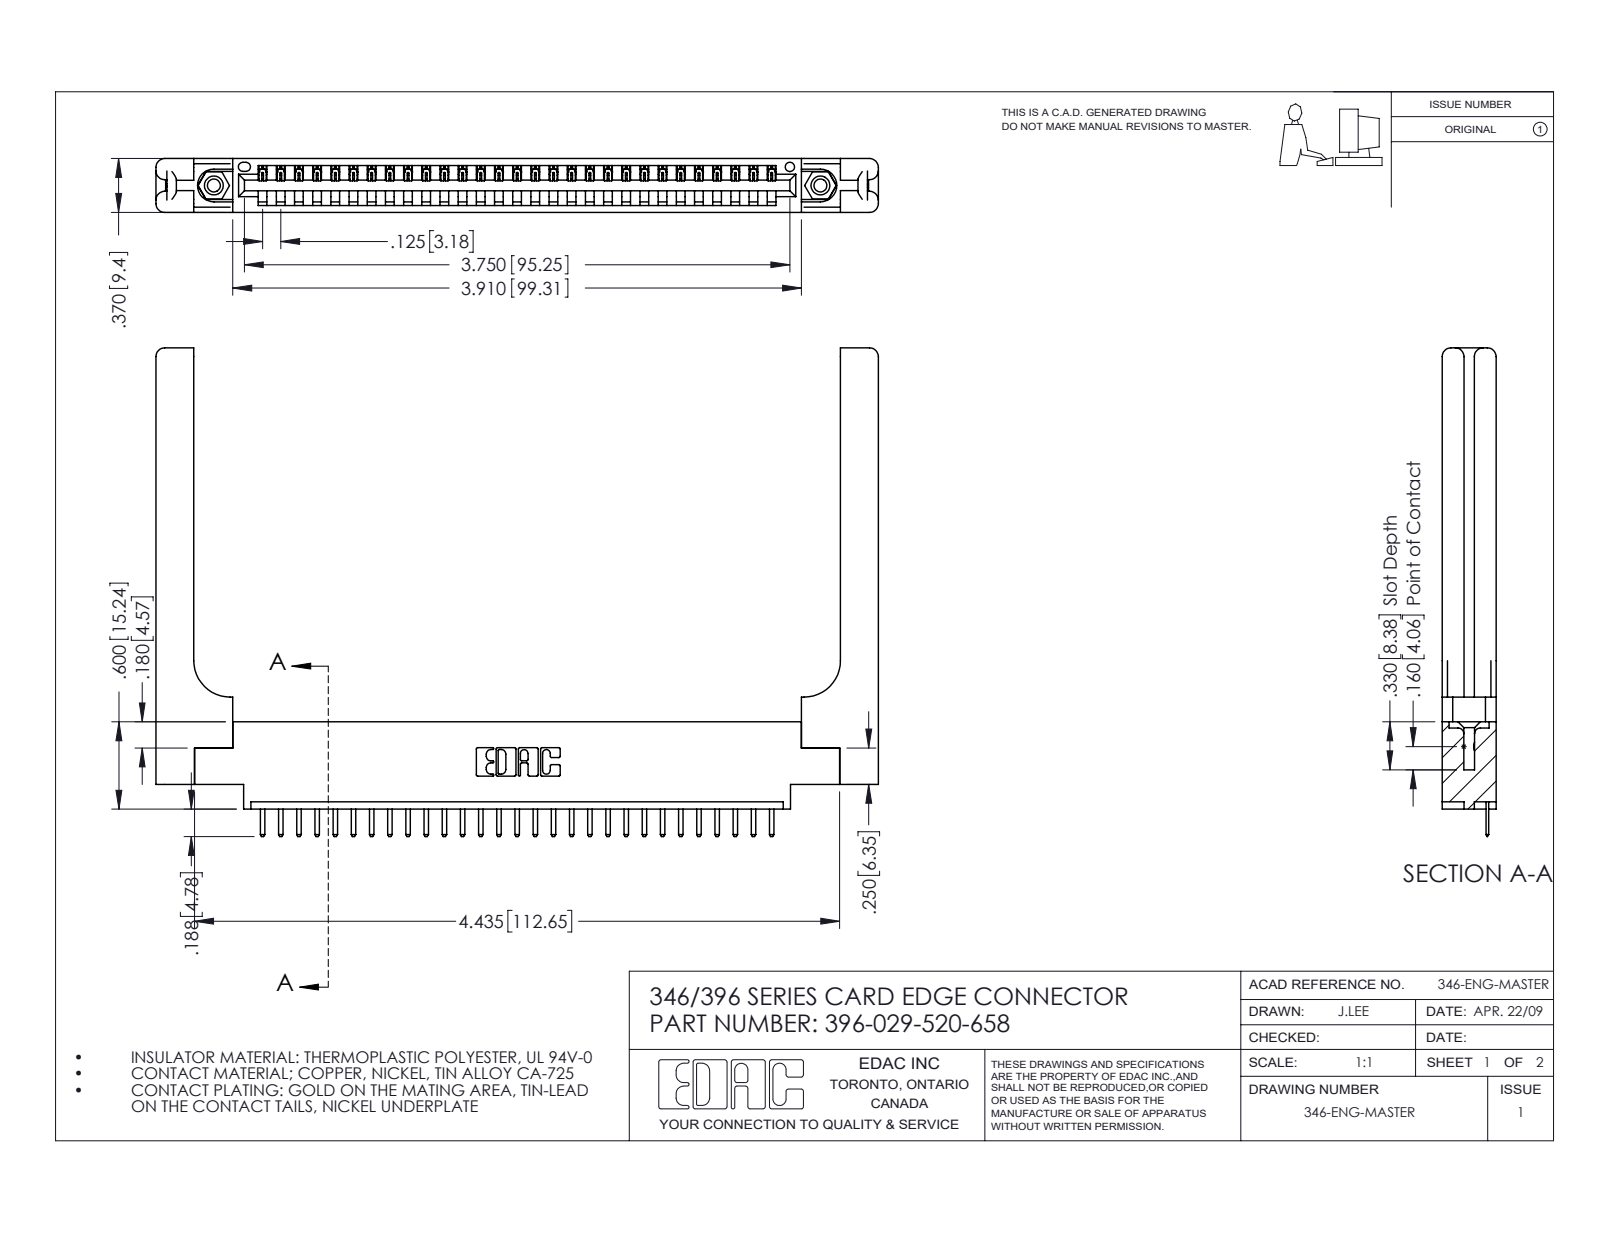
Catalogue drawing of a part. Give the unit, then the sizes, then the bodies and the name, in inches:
Units: inches
Overall size (bounding box): 4.966 × 3.358 × 0.37
Round holes (diameter × count): ⌀0.089 ×2, ⌀0.125 ×2, ⌀0.156 ×2, ⌀0.064 ×1
Round bosses / shafts (diameter × count): ⌀0.155 ×2
Partial cylindrical surfaces — rounded edges, fillets, slot ends (radius × count): R0.01 ×60, R0.006 ×58, R0.01 ×22, R0.06 ×16, R0.007 ×6, R0.031 ×6, R0.026 ×3, R0.03 ×2
Main face-to-face distances: 0.37, 0.072, 0.048, 0.322, 0.148, 0.15, 0.25, 0.298, 0.025, 0.076
Hole centre spacings: 0.246, 3.962, 4.17
Volume: 1.176 in³ · Surface area: 30.37 in²
Bodies: 34 solids, 2180 faces (1446 planar, 674 cylindrical, 60 other)
Part name (STEP PRODUCT): 346 Part_0.170 Offset - 0.156 Dia-TH; 346-220-058_345-220-058; 345-292-001_345-293-120; 345-250-001_345-250-001-102 (+1 more)
STEP written by: SolidWorks 2016 (CONFIG_CONTROL_DESIGN)
